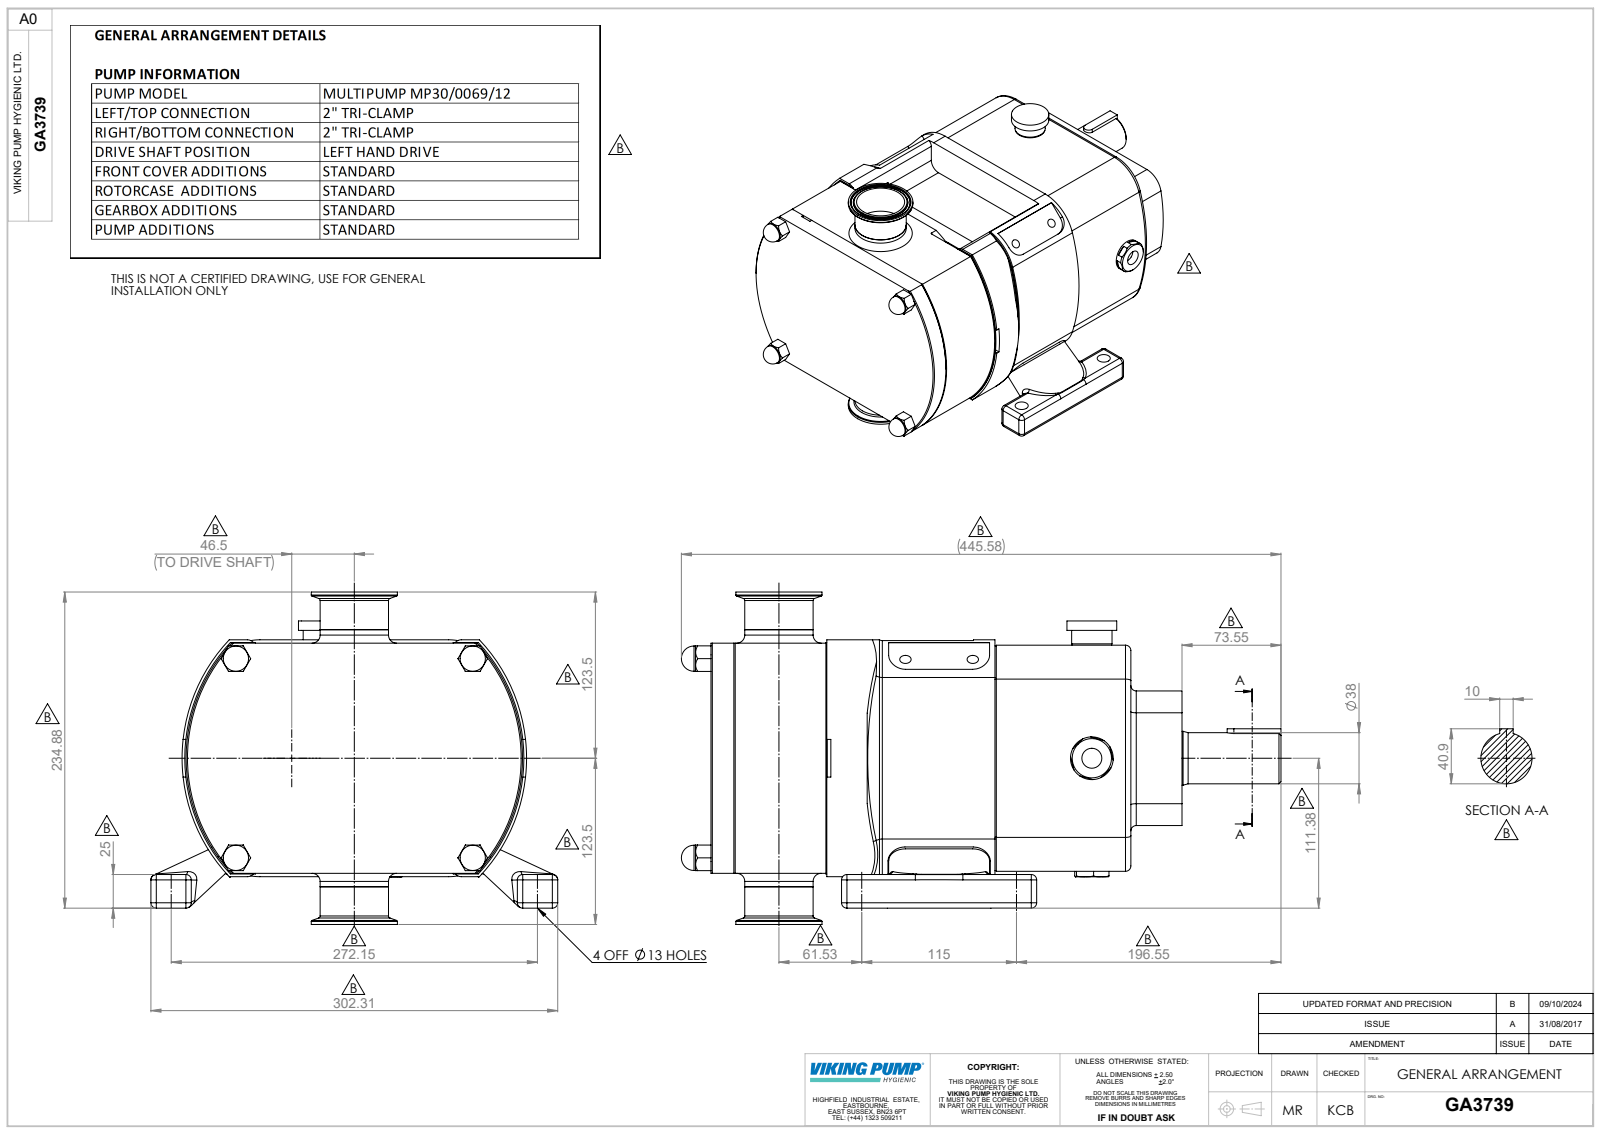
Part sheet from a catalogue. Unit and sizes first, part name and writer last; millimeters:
Units: millimetres
Overall size (bounding box): 445.58 × 302.31 × 247
Round holes (diameter × count): ⌀8.5 ×4, ⌀10.11 ×4, ⌀13 ×4, ⌀9.09 ×2, ⌀14.86 ×1, ⌀35 ×1, ⌀47.65 ×1
Round bosses / shafts (diameter × count): ⌀18.8 ×4, ⌀83 ×2, ⌀50 ×2, ⌀64 ×1, ⌀50.8 ×1, ⌀40.01 ×1, ⌀38 ×1, ⌀37 ×1
Partial cylindrical surfaces — rounded edges, fillets, slot ends (radius × count): R4 ×44, R1 ×16, R10 ×12, R6 ×10, R12.5 ×4, R12.57 ×4, R12.6 ×4, R20 ×4
Main face-to-face distances: 1.5, 169.5, 38, 139, 134.98, 29, 215.05, 350.03, 30.5, 140.5
Hole centre spacings: 63.64, 50.05, 70.13, 90, 90.11, 115, 149.42, 153.04
Volume: 11 470 000 mm³ · Surface area: 531 110 mm²
Bodies: 5 solids, 740 faces (269 planar, 242 cylindrical, 229 other)
Part name (STEP PRODUCT): GA3739; CP30-0069-12 V L; Z94-5121-33 - 2 INCH
STEP written by: SolidWorks 2023 (AUTOMOTIVE_DESIGN)
